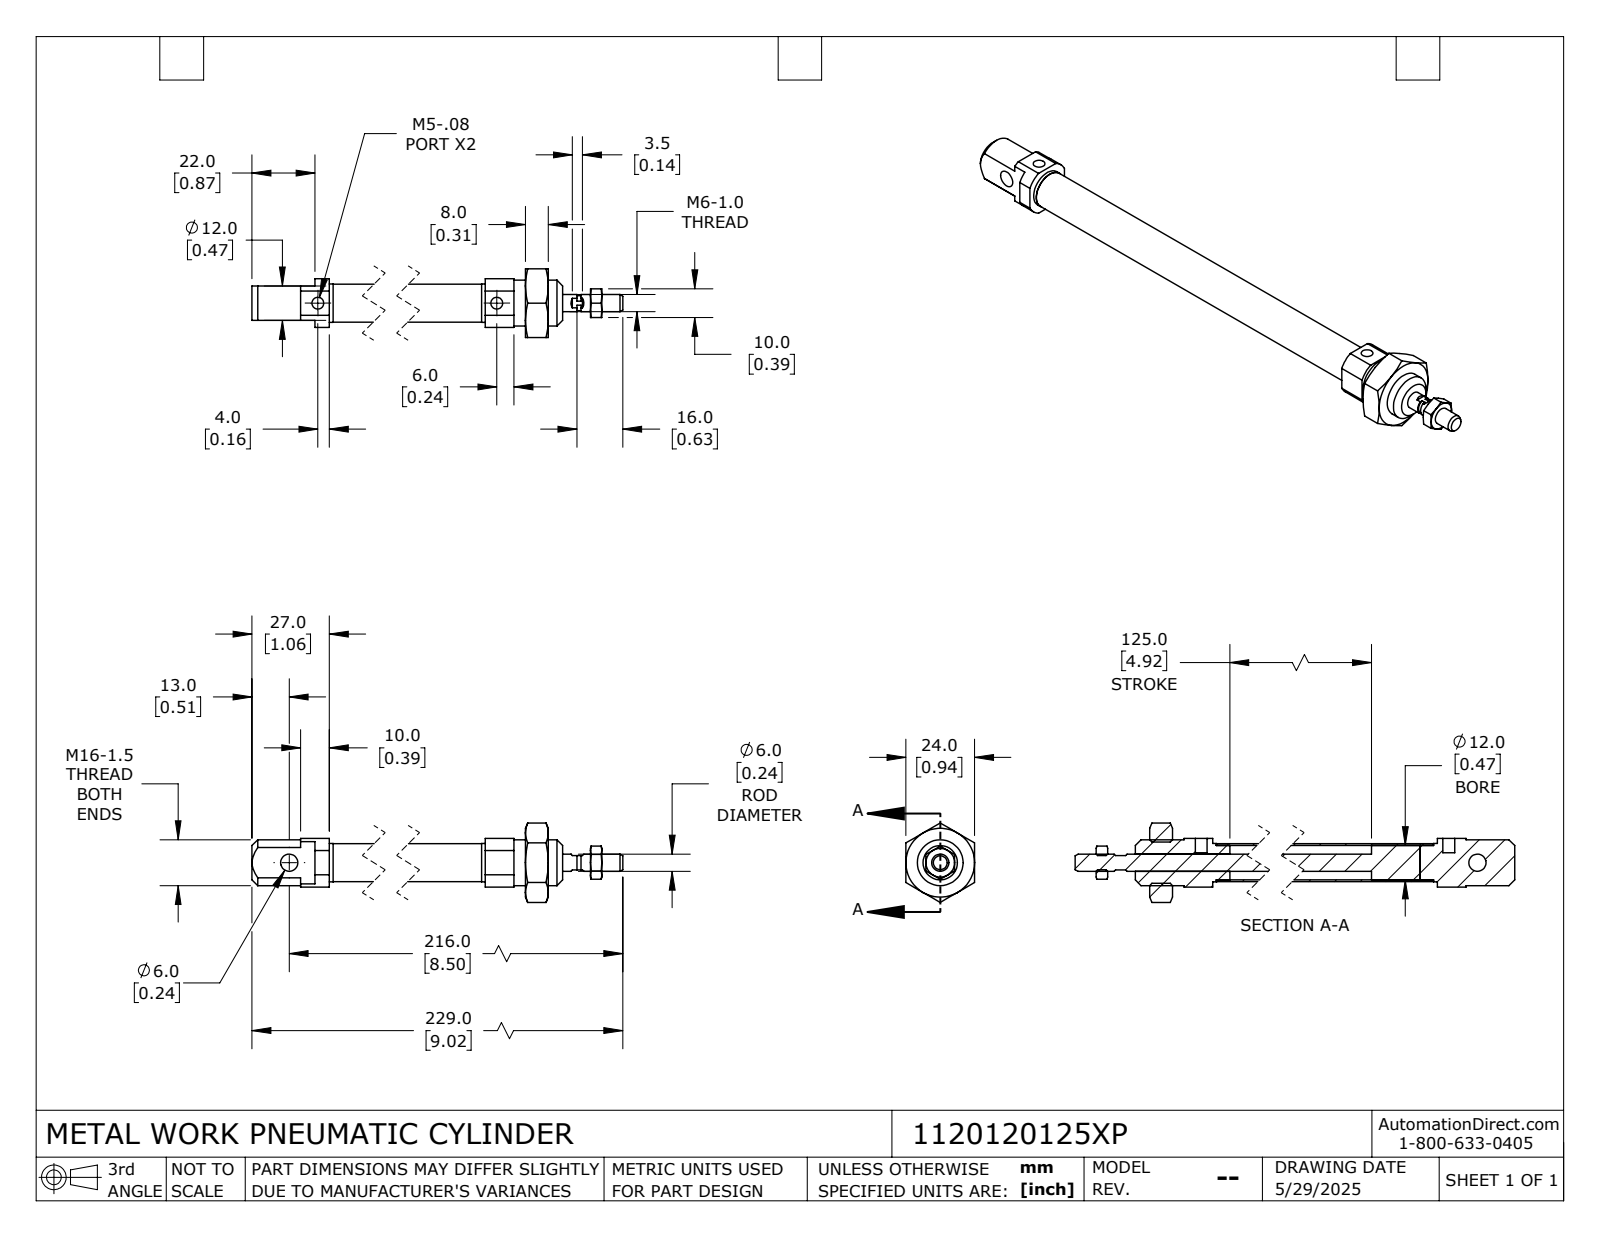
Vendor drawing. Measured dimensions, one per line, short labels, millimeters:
name: 1120120125XP_ROD; 1120120125XP; 1120120125XP_BODY
written by: SolidWorks 2024 (CONFIG_CONTROL_DESIGN)
unit: mm
bodies: 6 solids, 139 faces (56 planar, 45 cylindrical, 38 other)
size: 229 × 27.71 × 24
volume: 24 811 mm³; area: 23 341 mm²
holes: 2× ⌀4.13, 1× ⌀4.92, 1× ⌀6, 1× ⌀14.38
bosses: 1× ⌀16, 1× ⌀13.4, 1× ⌀13.27, 1× ⌀12, 1× ⌀6, 1× ⌀5.2
rounds: 1× R9.5
face distances: 17, 6, 24, 12, 181, 2.5, 14.5, 8, 3.5, 33
hole spacings: 162
